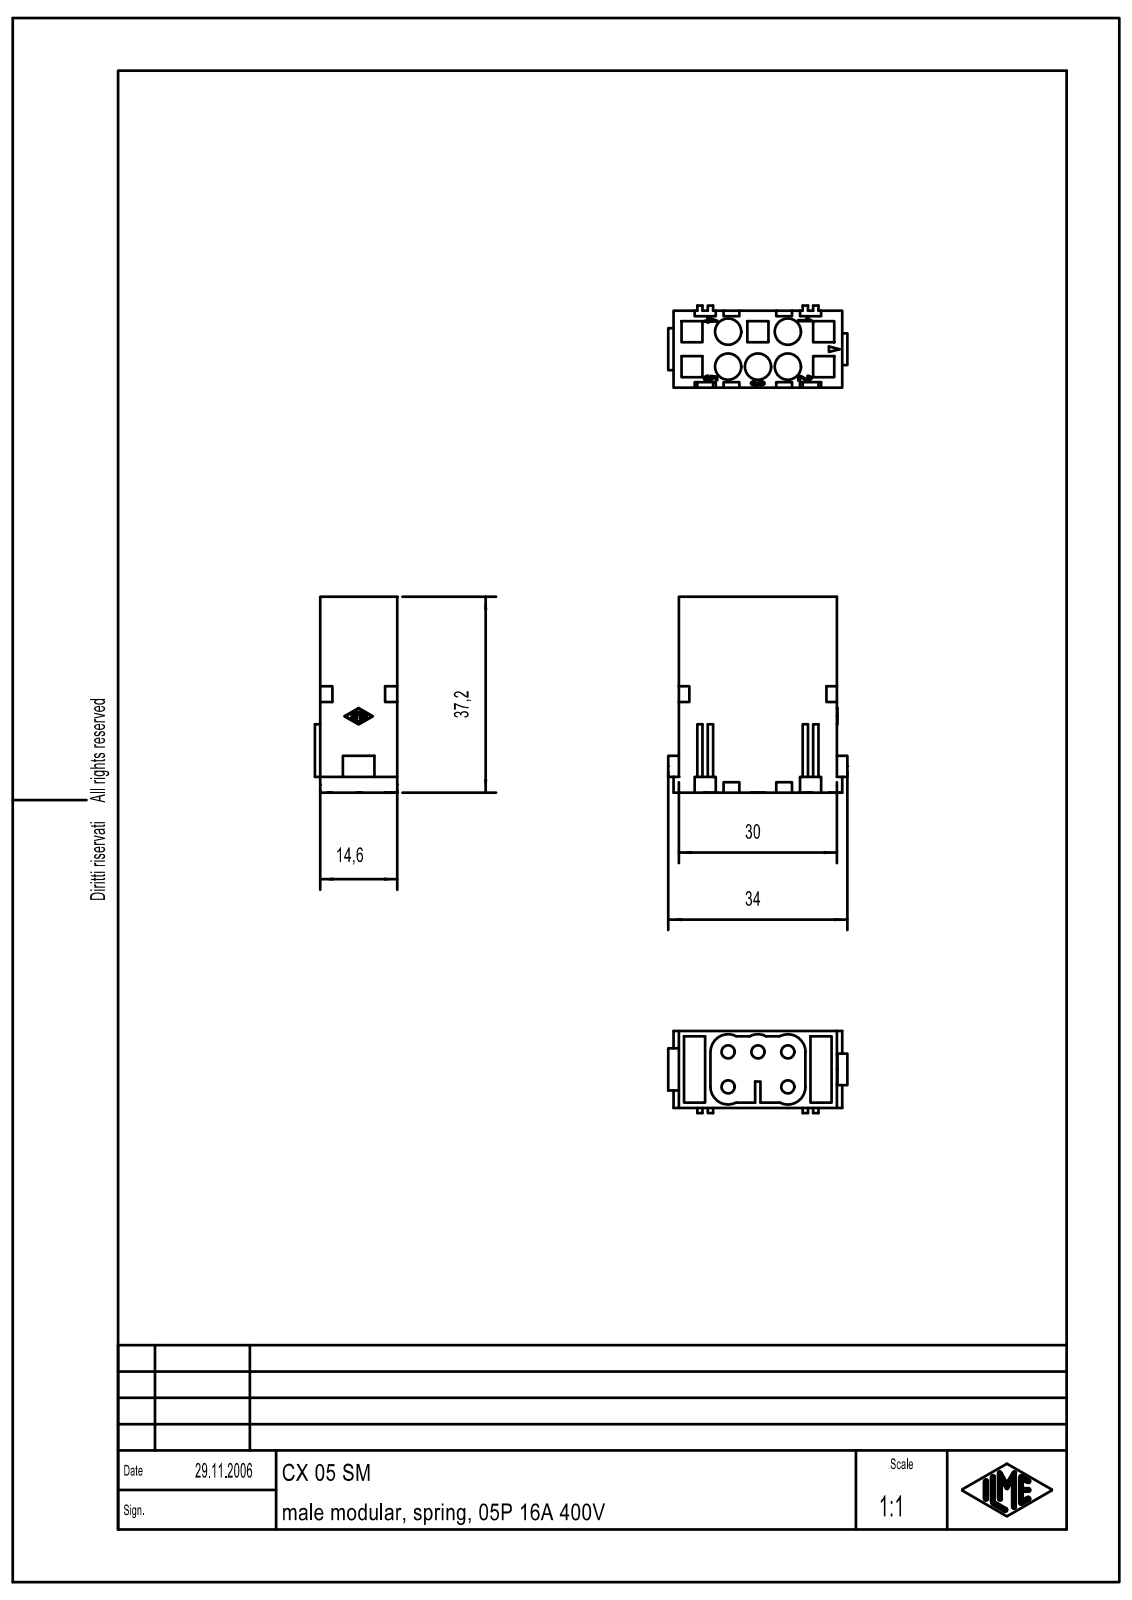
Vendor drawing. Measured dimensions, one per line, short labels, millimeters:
name: CX_05_SM
written by: Creo Elements/Direct Modeling 20.1B 02-Apr-2019 (C) Parametric Technology GmbH (AUTOMOTIVE_DESIGN)
unit: mm
bodies: 1 solid, 1766 faces (1616 planar, 90 cylindrical, 60 other)
size: 37.2 × 34 × 15.6
volume: 10 893 mm³; area: 8 439 mm²
holes: 5× ⌀5
bosses: 5× ⌀2.5
rounds: 14× R0.2, 12× R0.5, 5× R3.25, 4× R0.1, 4× R0.3, 4× R1, 4× R4.25, 1× R0.19
face distances: 14.7, 1, 30, 5.1, 23.9, 29, 24.9, 6.1, 22.9, 4.1
hole spacings: 6.42, 6.65, 8.84, 12.8, 14.42
